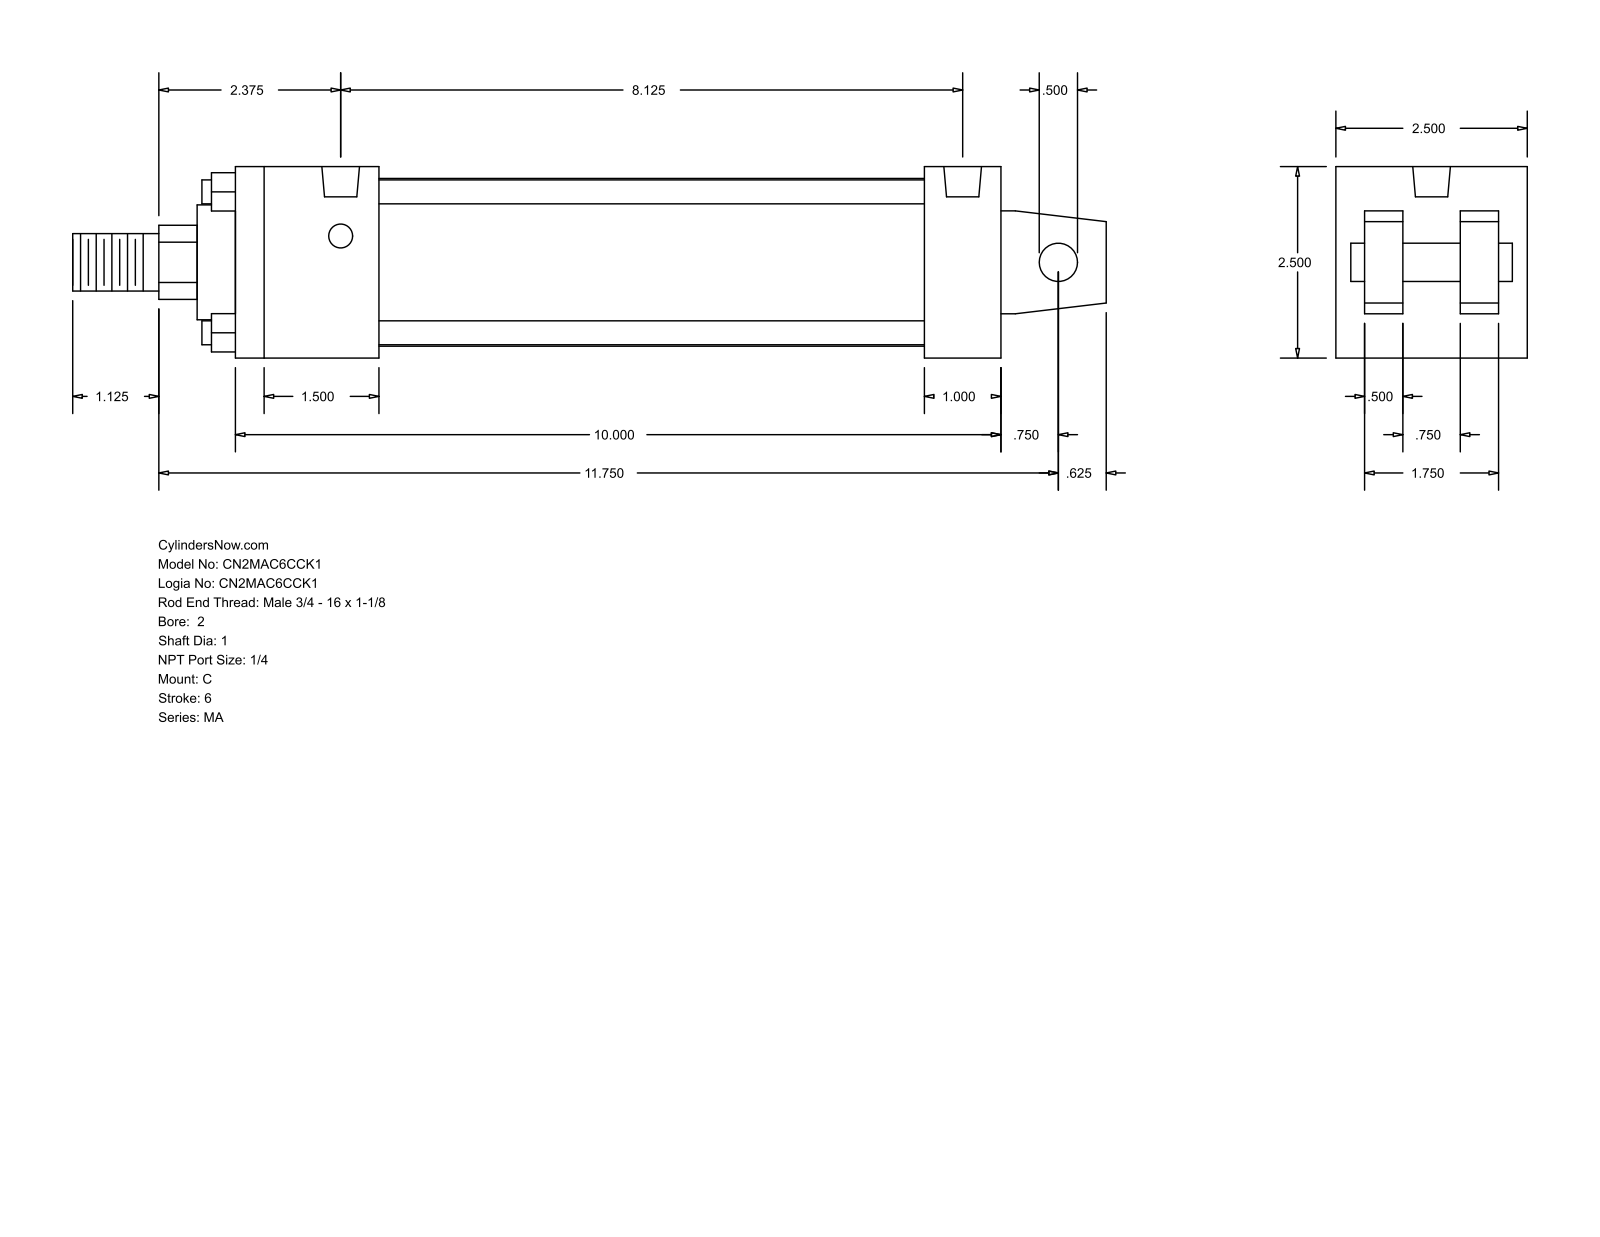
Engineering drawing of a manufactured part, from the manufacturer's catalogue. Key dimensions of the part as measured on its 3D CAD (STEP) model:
Part name (STEP PRODUCT): MA_C__0200_1
STEP written by: GSSL Pune (CONFIG_CONTROL_DESIGN)
Units: millimetres
Bodies: 0 solids, 103 faces (76 planar, 27 cylindrical, 0 other)
Overall size (bounding box): 342.9 × 63.5 × 63.5
Round holes (diameter × count): ⌀7.94 ×4, ⌀12.49 ×2
Round bosses / shafts (diameter × count): ⌀7.94 ×4, ⌀55.63 ×1, ⌀38.1 ×1, ⌀25.4 ×1, ⌀19.05 ×1, ⌀12.7 ×1
Partial cylindrical surfaces — rounded edges, fillets, slot ends (radius × count): R12.29 ×1
Main face-to-face distances: 63.5, 12.7, 254, 22.22, 41.28, 9.52, 53.98, 31.76, 47.63, 25.4
Hole centre spacings: 206.37
